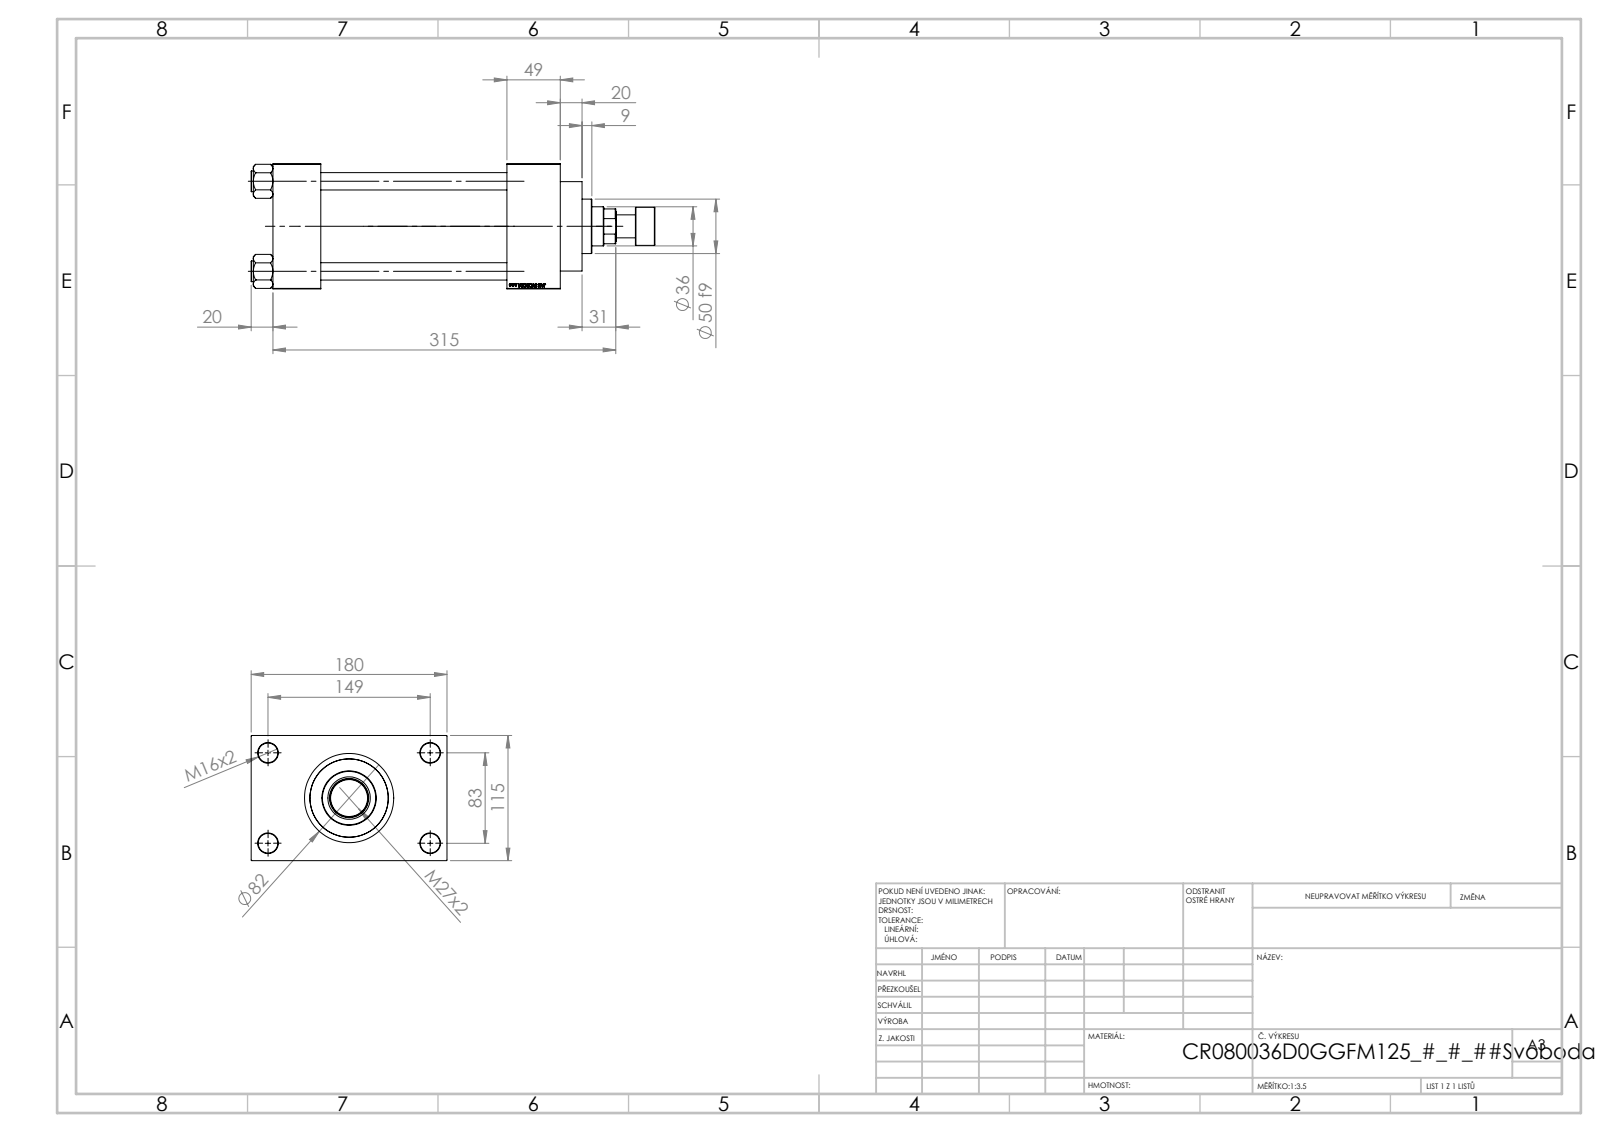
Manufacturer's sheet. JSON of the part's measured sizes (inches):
{"part_name": "V215_VC_A; V215CR_ROD_END_F; NUT_M5_D; V215CR_VCP_D (+2 more)", "step_written_by": "SolidWorks 2019 (CONFIG_CONTROL_DESIGN)", "units": "inches", "bodies": {"solids": 12, "faces": 1166, "planar": 549, "cylindrical": 93, "other": 524}, "overall_size": [14.606, 7.087, 4.528], "volume_in3": 140, "surface_area_in2": 600.2, "round_holes": [[0.63, 4], [0.709, 4], [0.276, 2], [1.041, 2], [1.378, 2], [1.004, 1], [1.417, 1], [1.535, 1], [2.402, 1], [2.835, 1], [3.15, 1]], "round_bosses_or_shafts": [[0.748, 4], [3.386, 1], [3.228, 1], [1.969, 1], [1.378, 1], [0.827, 1]], "face_to_face_distances": [4.528, 6.732, 1.929, 8.661, 1.732, 8.465, 10.394, 1.28, 5.807, 7.087], "hole_center_spacings": [1.305, 2.302, 3.256, 3.357, 3.513, 4.561, 5.607, 3.268]}
